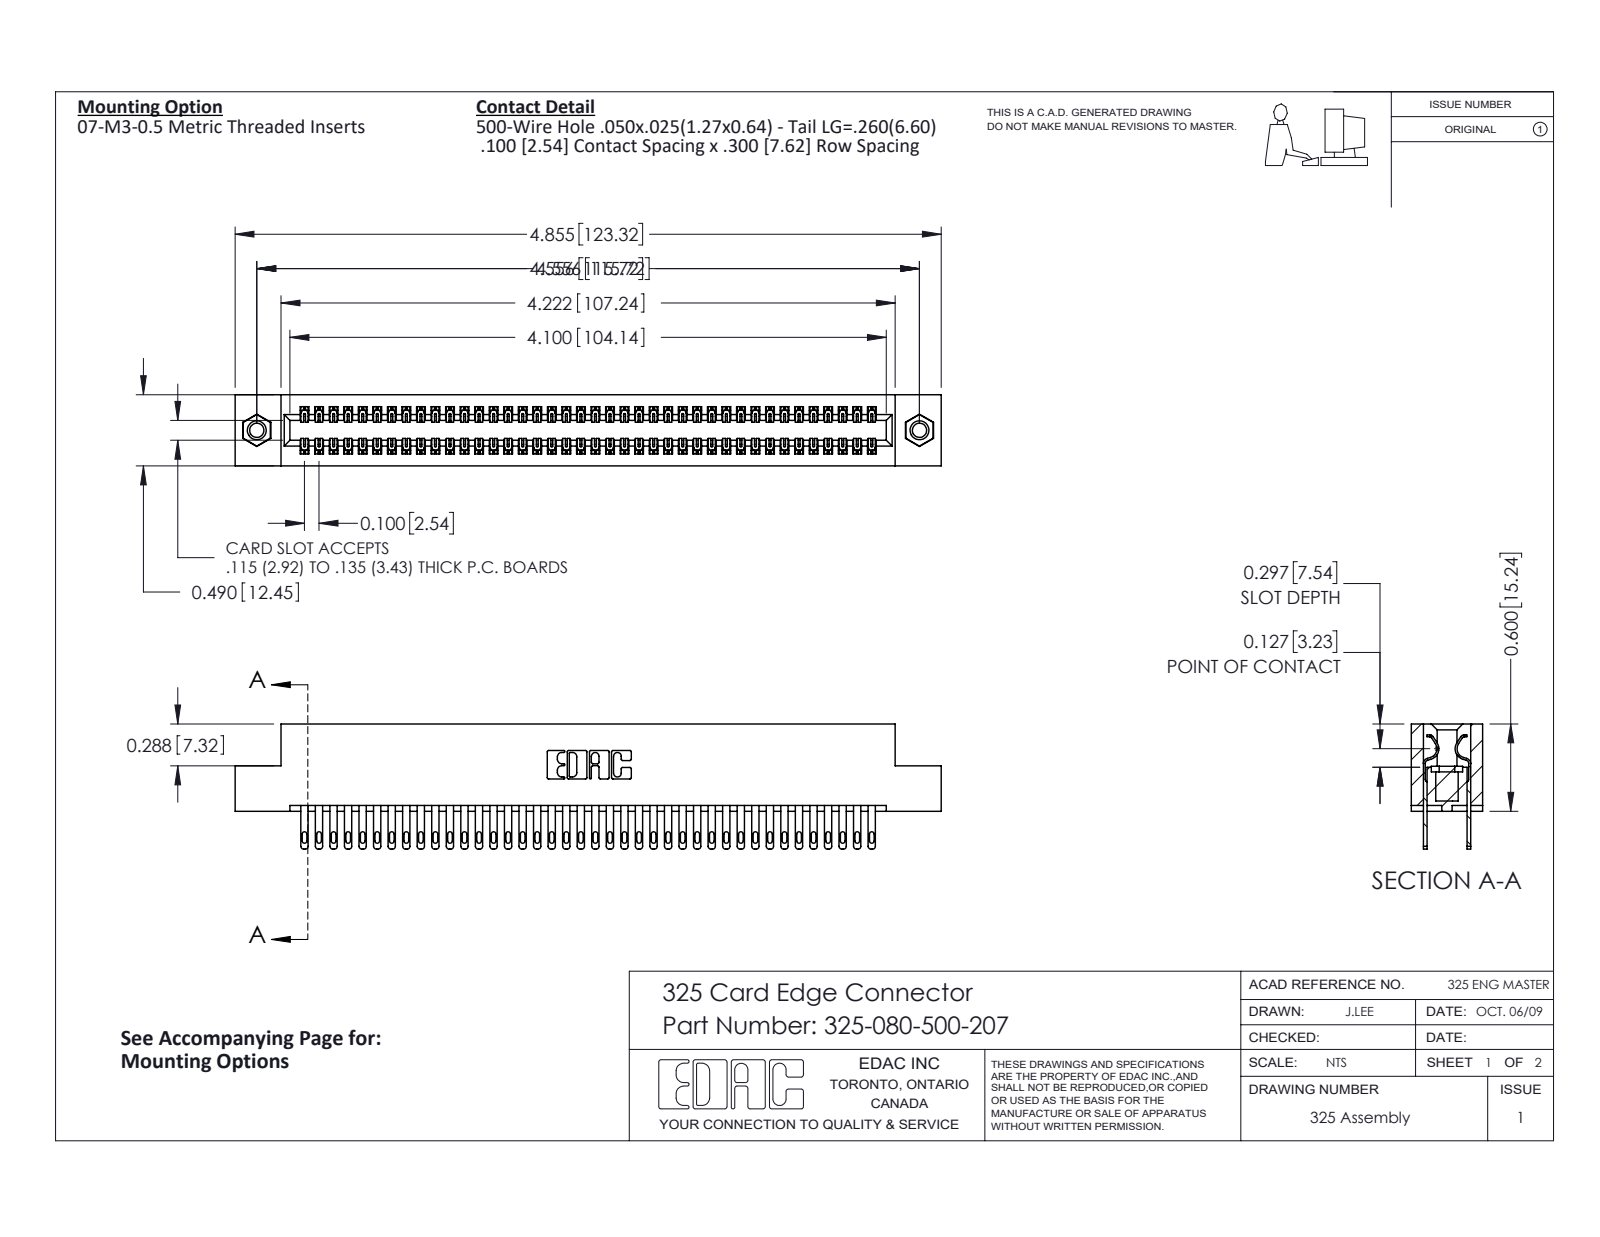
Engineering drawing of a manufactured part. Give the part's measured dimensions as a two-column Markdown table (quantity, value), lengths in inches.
| quantity | value |
| --- | --- |
| part name | 325 Part_TI; 325-292-001_325-293-100; 345-250-001_345-250-005-103; 325-080-500-207 |
| STEP written by | SolidWorks 2016 (CONFIG_CONTROL_DESIGN) |
| units | inches |
| bodies | 83 solids, 4014 faces (2502 planar, 1496 cylindrical, 16 other) |
| overall size | 4.855 × 0.86 × 0.49 |
| volume | 0.984 in³ |
| surface area | 31.53 in² |
| round holes (diameter × count) | 0.098 × 2, 0.125 × 2, 0.16 × 2 |
| round bosses / shafts (diameter × count) | 0.155 × 2 |
| partial cylindrical surfaces (radius × count) | 0.006 × 120, 0.016 × 80, 0.02 × 80, 0.01 × 22, 0.007 × 6, 0.031 × 6, 0.026 × 3, 0.014 × 2 |
| main face-to-face distances | 0.083, 0.407, 0.3, 0.107, 0.383, 0.025, 0.49, 0.325, 0.275, 0.56 |
| hole center spacings | 4.556 |
